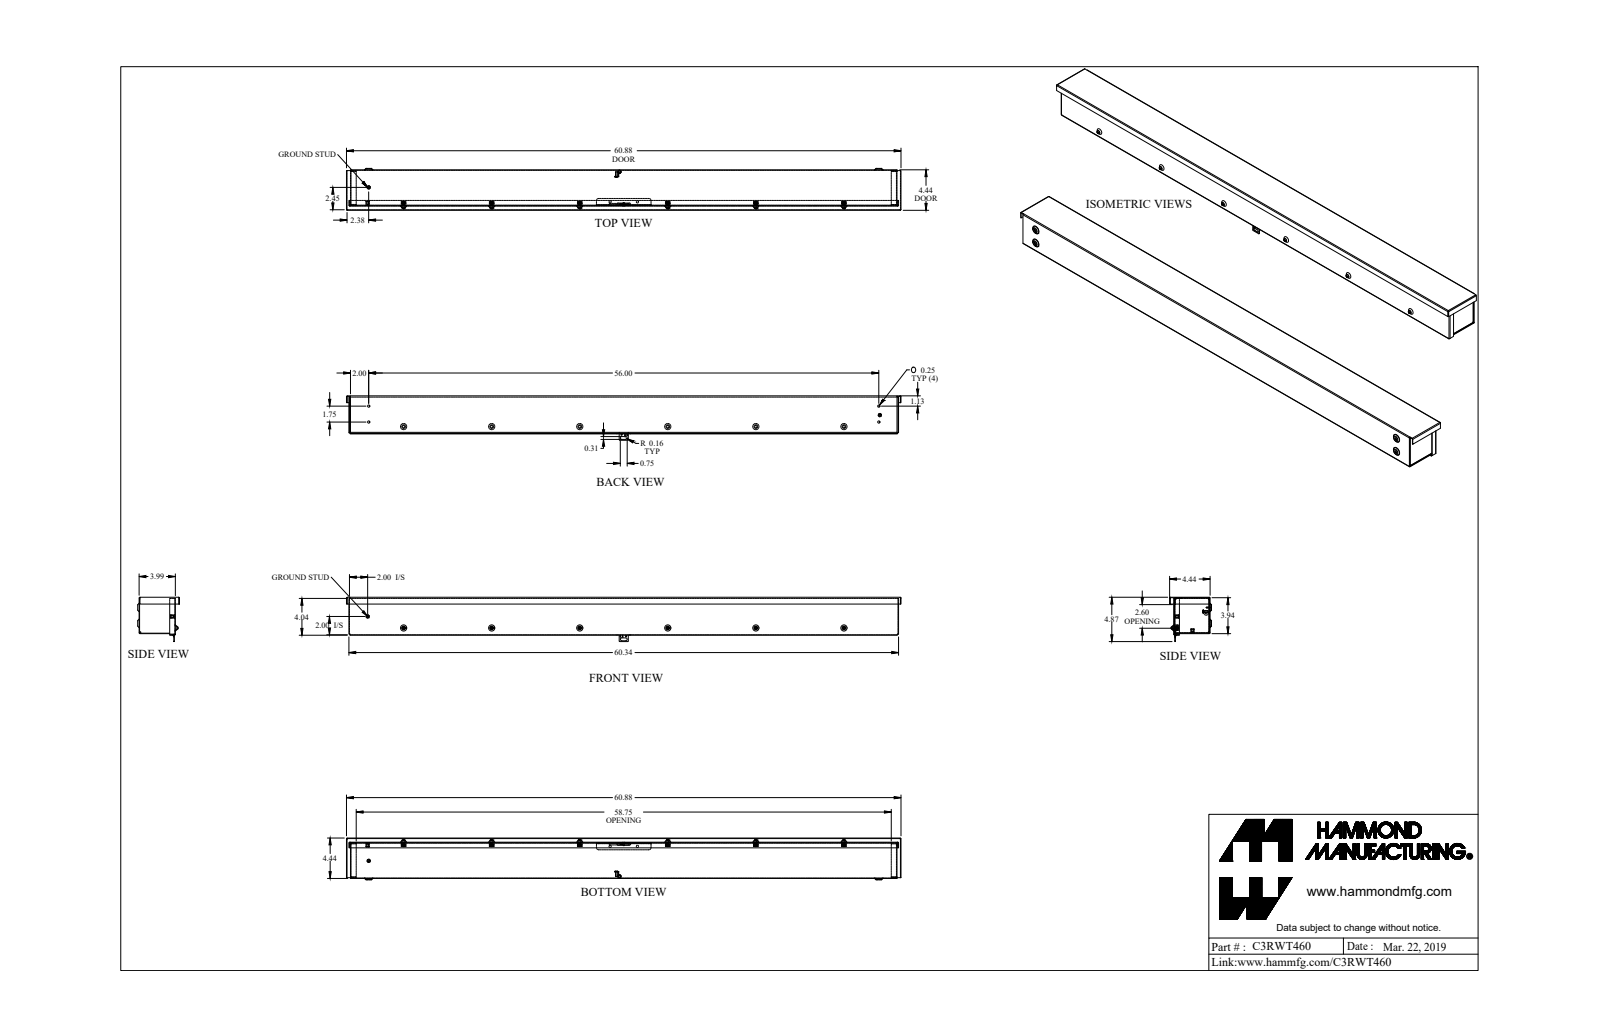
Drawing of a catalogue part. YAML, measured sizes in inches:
part_name: "C3RWT460_Default"
step_written_by: "SolidWorks 2019 (CONFIG_CONTROL_DESIGN)"
units: inches
bodies: {solids: 31, faces: 1129, planar: 628, cylindrical: 353, other: 148}
overall_size: [60.875, 4.871, 4.594]
volume: 67.18
surface_area: 2379
round_holes:
  - {diameter: 0.156, count: 8}
  - {diameter: 0.214, count: 6}
  - {diameter: 0.23, count: 6}
  - {diameter: 0.25, count: 6}
  - {diameter: 0.203, count: 2}
  - {diameter: 0.125, count: 1}
  - {diameter: 0.137, count: 1}
  - {diameter: 0.2, count: 1}
  - {diameter: 0.215, count: 1}
round_bosses_or_shafts:
  - {diameter: 0.19, count: 7}
  - {diameter: 0.148, count: 6}
  - {diameter: 0.375, count: 2}
  - {diameter: 0.5, count: 1}
  - {diameter: 0.367, count: 1}
  - {diameter: 0.21, count: 1}
  - {diameter: 0.152, count: 1}
  - {diameter: 0.125, count: 1}
partial_cylinders:
  - {radius: 0.08, count: 24}
  - {radius: 0.108, count: 24}
  - {radius: 0.029, count: 18}
  - {radius: 0.086, count: 18}
  - {radius: 0.125, count: 16}
  - {radius: 0.022, count: 12}
  - {radius: 0.171, count: 6}
  - {radius: 0.206, count: 6}
face_to_face_distances: [0.057, 3.928, 3.943, 3.871, 3.886, 3.985, 4, 4.381, 0.51, 0.453]
hole_center_spacings: [9.669, 29.006, 19.337, 19.338, 38.675, 4.837, 8.09, 9.669]
